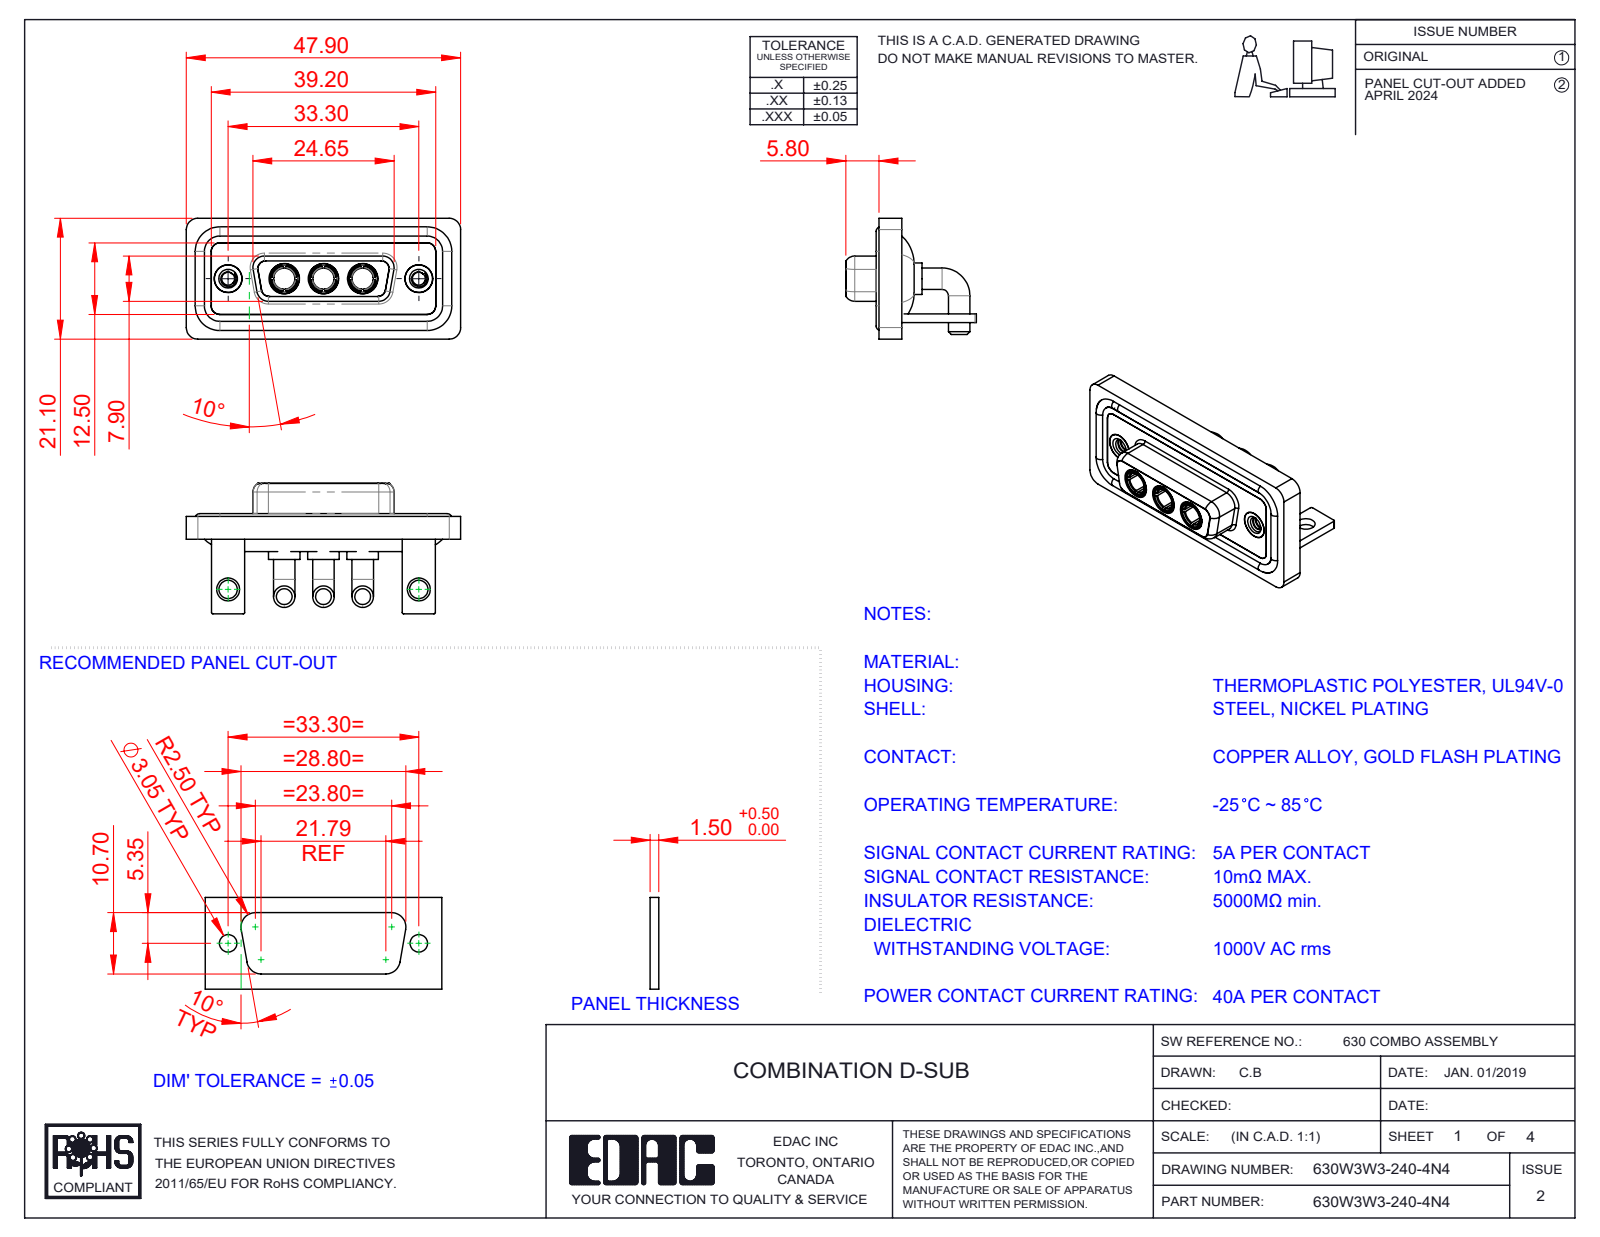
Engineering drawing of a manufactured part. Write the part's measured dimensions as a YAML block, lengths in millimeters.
part_name: "630Combo Shell Rear_15 Contacts; 630Combo Housing_3W3; 630Combo Shell Front_15 Contacts; 630Combo Stabilizer Bracket_50 Contacts (+4 more)"
step_written_by: "SolidWorks 2023 (CONFIG_CONTROL_DESIGN)"
units: millimeters
bodies: {solids: 15, faces: 668, planar: 212, cylindrical: 287, other: 169}
overall_size: [47.9, 22.8, 21.1]
volume: 6765
surface_area: 10838
round_holes:
  - {diameter: 4.85, count: 5}
  - {diameter: 3.7, count: 3}
  - {diameter: 5.3, count: 3}
  - {diameter: 2.26, count: 2}
  - {diameter: 3.2, count: 2}
  - {diameter: 4, count: 2}
  - {diameter: 4.05, count: 2}
  - {diameter: 5, count: 2}
round_bosses_or_shafts:
  - {diameter: 3.75, count: 6}
  - {diameter: 1.6, count: 4}
  - {diameter: 5.5, count: 3}
  - {diameter: 5.2, count: 3}
  - {diameter: 4.96, count: 3}
  - {diameter: 4.75, count: 3}
  - {diameter: 4.95, count: 2}
  - {diameter: 4.8, count: 2}
partial_cylinders:
  - {radius: 2, count: 21}
  - {radius: 1.5, count: 18}
  - {radius: 0.25, count: 16}
  - {radius: 1.35, count: 12}
  - {radius: 1.6, count: 8}
  - {radius: 0.5, count: 5}
  - {radius: 0.6, count: 4}
  - {radius: 0.65, count: 4}
face_to_face_distances: [0.4, 2.9, 1.5, 1.8, 3.7, 1.1, 4.1, 1.6, 2.5, 1.4]
hole_center_spacings: [6.85, 9.8, 16.65, 23.5, 33.3, 13.7]
